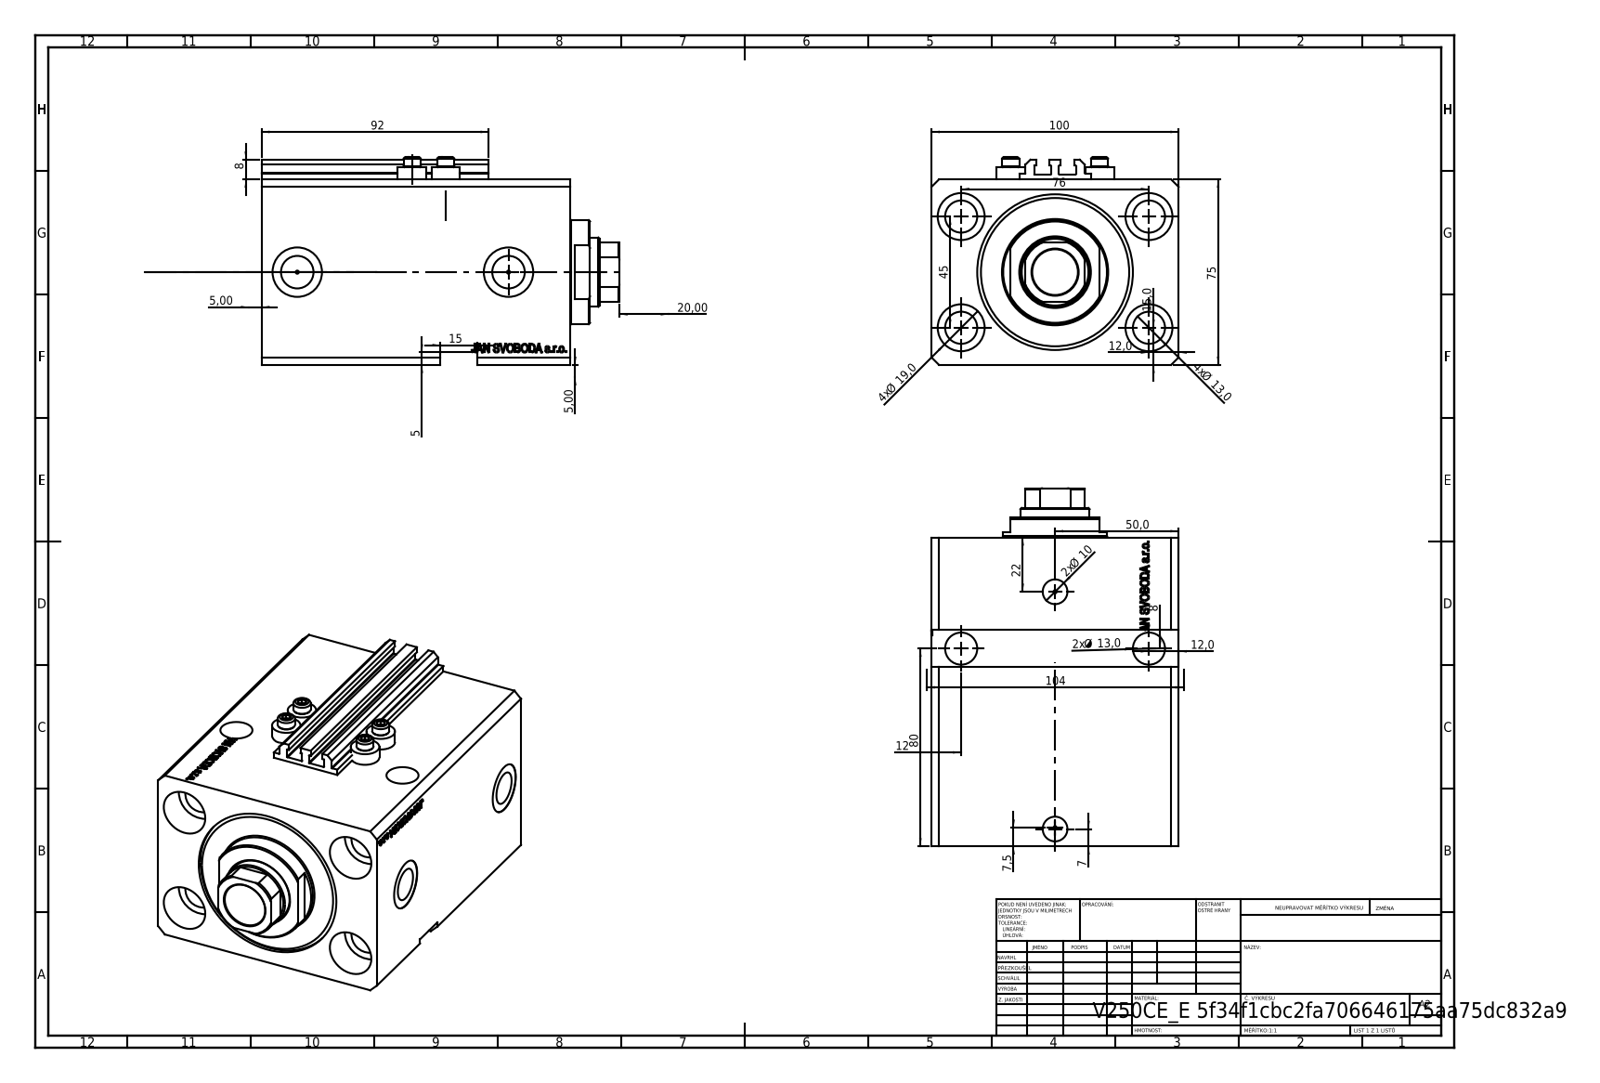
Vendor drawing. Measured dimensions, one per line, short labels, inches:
name: ALLEN BOLT V250CE; V250CE_C_VCP; V250CE_E_Body; V250CE_VC_E
written by: SolidWorks 2019 (CONFIG_CONTROL_DESIGN)
unit: in
bodies: 8 solids, 1104 faces (539 planar, 138 cylindrical, 427 other)
size: 5.705 × 3.937 × 3.307
volume: 47.55 in³; area: 232.9 in²
holes: 6× ⌀0.512, 4× ⌀0.049, 4× ⌀0.157, 4× ⌀0.748, 2× ⌀0.394, 2× ⌀0.518, 2× ⌀0.787, 1× ⌀0.728, 1× ⌀1.102, 1× ⌀1.969, 1× ⌀2.48
bosses: 4× ⌀0.457, 4× ⌀0.276, 1× ⌀1.654
rounds: 10× R0.008, 1× R0.531
face distances: 2.953, 3.937, 4.921, 0.469, 4.453, 3.874, 3.406, 1.047, 1.906, 0.512
hole spacings: 1.739, 2.992, 0.535, 0.816, 1.086, 1.324, 1.417, 1.515
